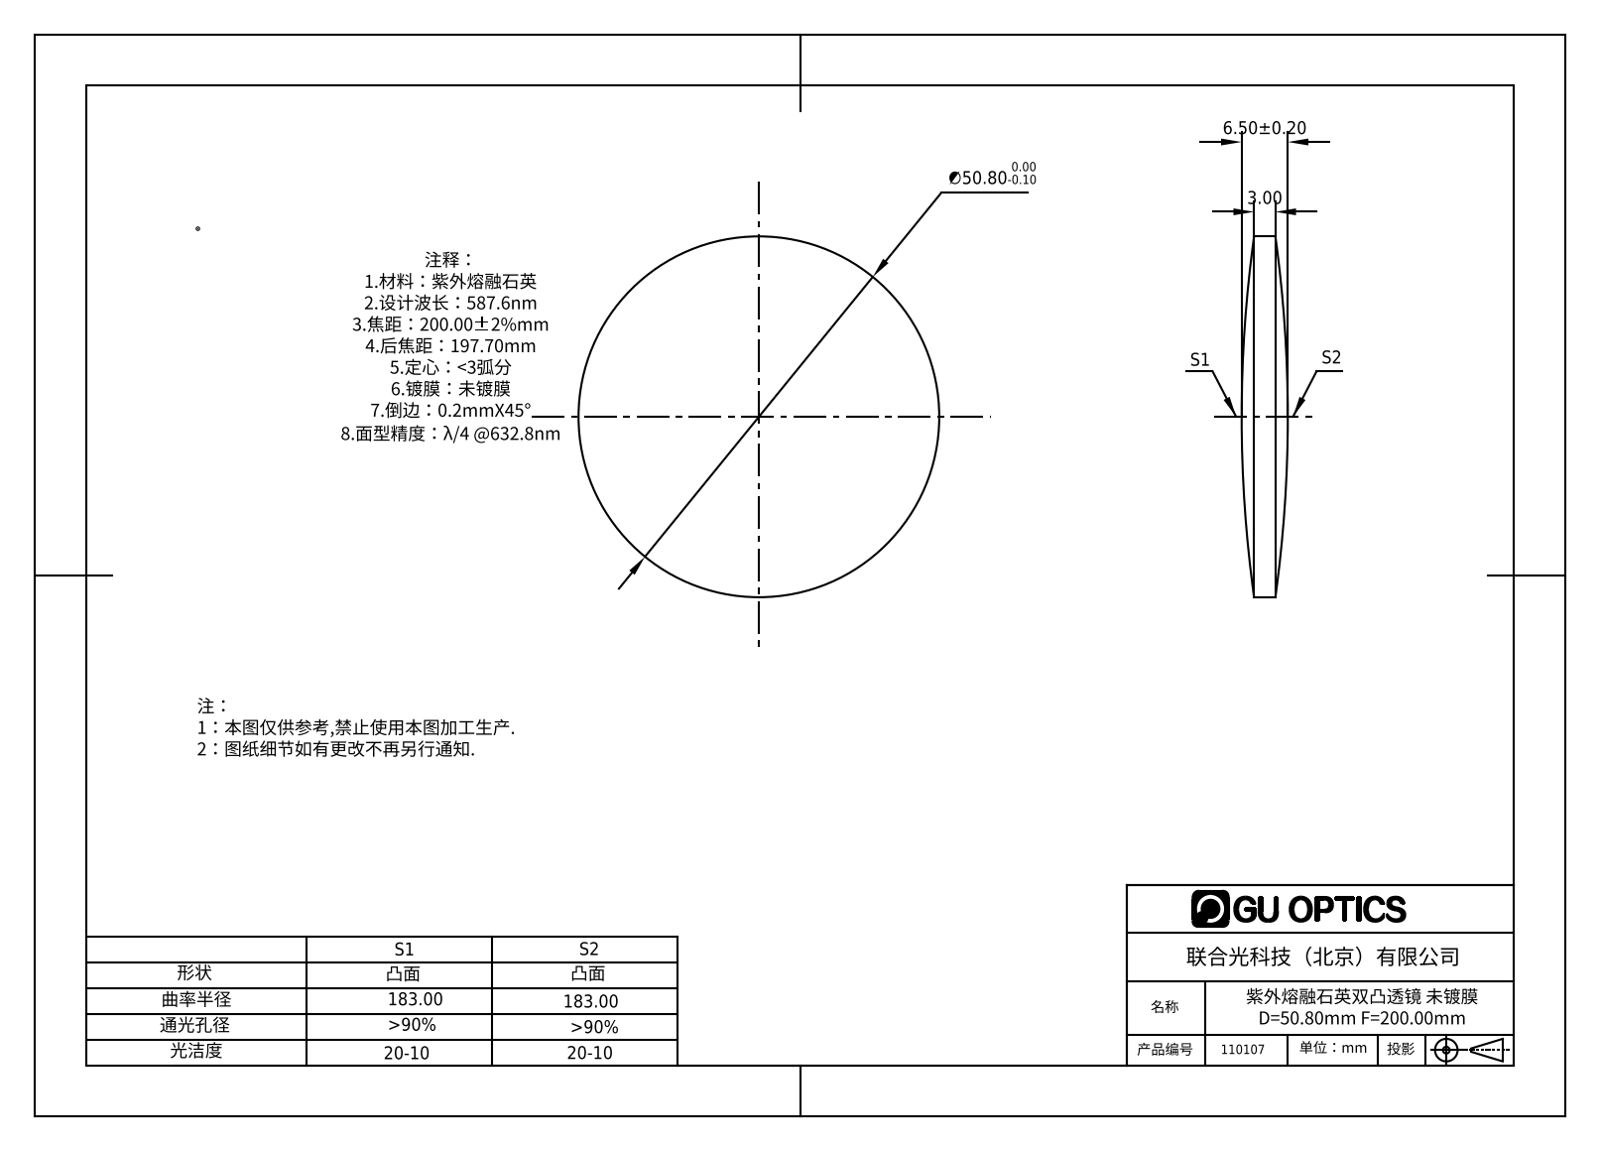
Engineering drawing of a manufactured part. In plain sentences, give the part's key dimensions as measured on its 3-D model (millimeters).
The part is named "110107". Its 3-D file was written by "SolidWorks 2016 (CONFIG_CONTROL_DESIGN)". It is 1 solid with 6 faces: 0 planar, 2 cylindrical and 4 other. Overall it measures 50.8 by 50.8 by 6.5 millimeters. Its volume is 9 633 cubic millimeters and its surface area 4 552 square millimeters. Round bosses or shafts: 1 of diameter 50.8.
